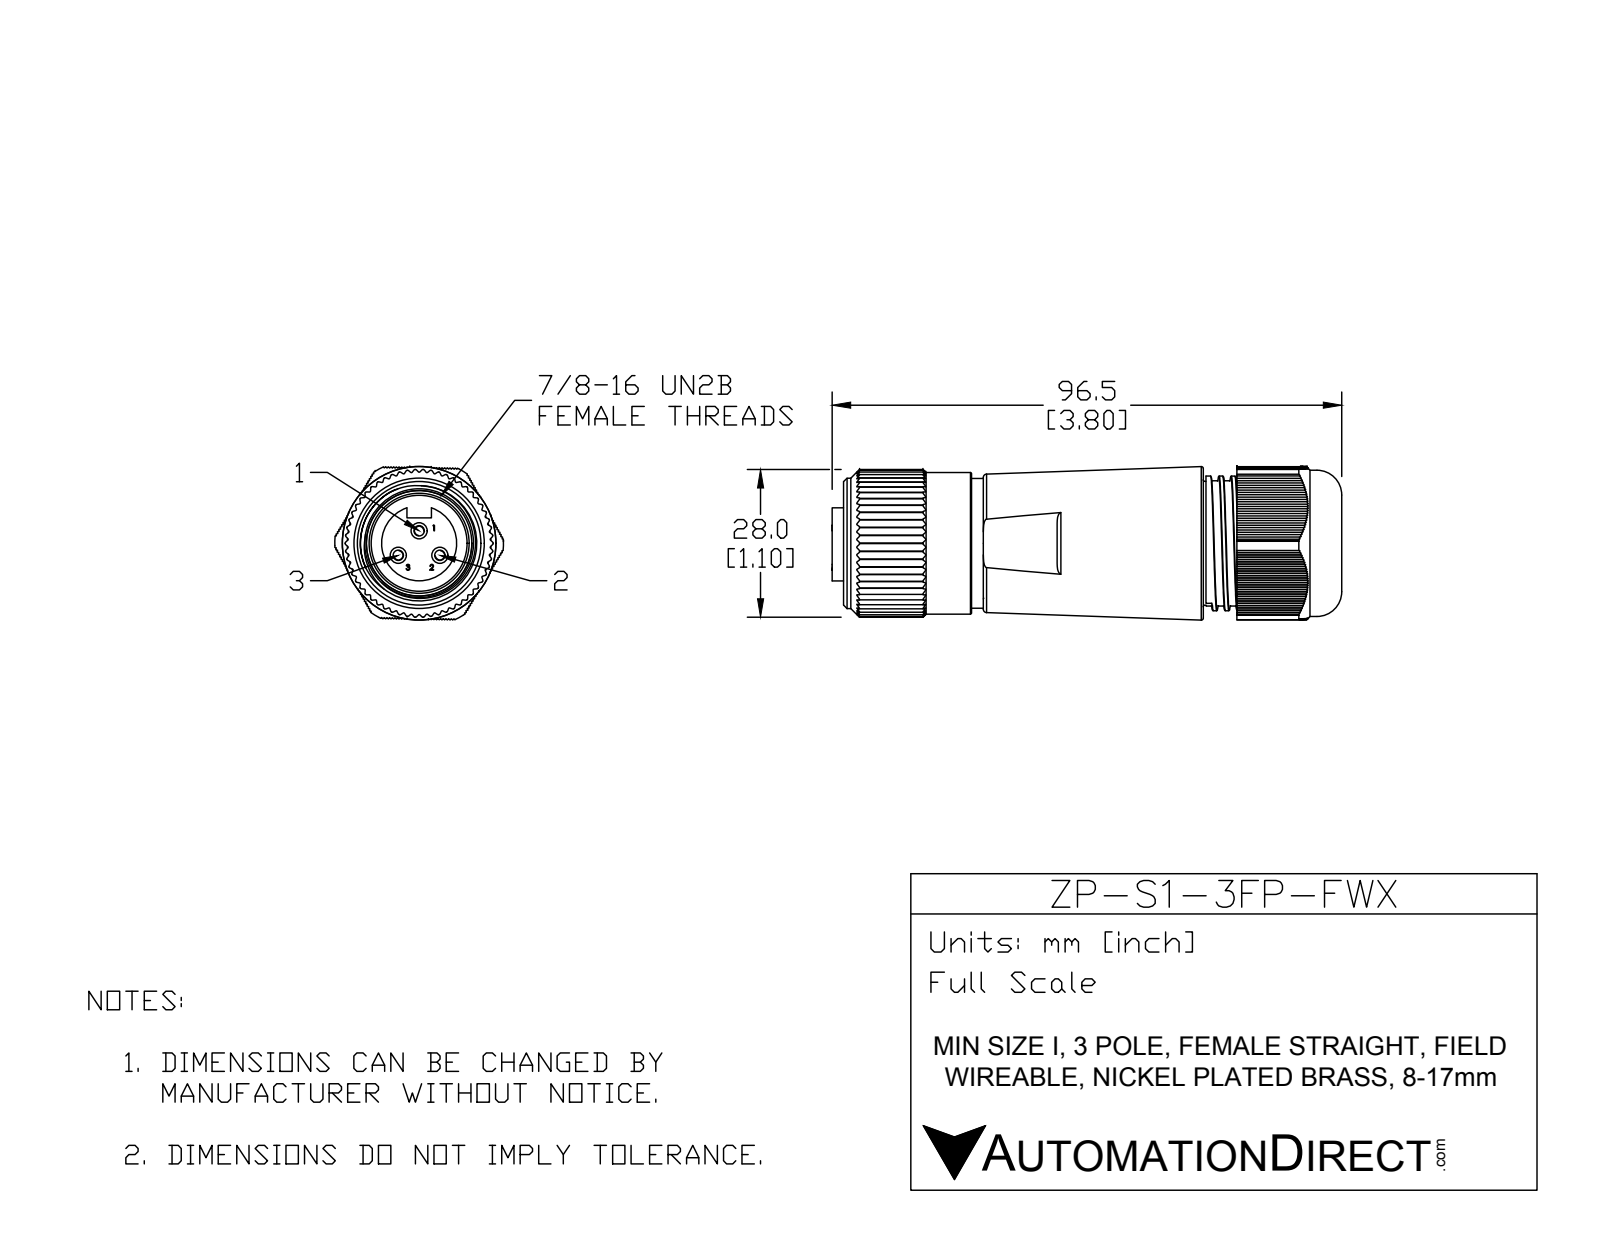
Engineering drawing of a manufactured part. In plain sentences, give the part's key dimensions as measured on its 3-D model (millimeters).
The part is named "MIN-3FP-FWX". Its 3-D file was written by "SolidWorks 2015 (AUTOMOTIVE_DESIGN)". It is 1 solid with 1065 faces: 669 planar, 335 cylindrical and 61 other. Overall it measures 96.54 by 31.9 by 29.06 millimeters. Its volume is 53 715 cubic millimeters and its surface area 15 695 square millimeters. Round holes: 3 of diameter 3.05, 1 of diameter 3.5, 1 of diameter 17.27, 1 of diameter 20.57, 1 of diameter 24.13, 1 of diameter 25.4. Round bosses or shafts: 1 of diameter 27.69, 1 of diameter 26.8, 1 of diameter 25.5, 1 of diameter 24.68, 1 of diameter 24.56, 1 of diameter 24, 1 of diameter 18.14, 1 of diameter 14.22. Partial cylindrical surfaces (rounded edges, fillets, slot ends): 116 of radius 0.25, 58 of radius 0.2, 1 of radius 14, 1 of radius 15.95. The main face-to-face distances are 0.36, 0.72, 1.08, 18.94, 18.92, 1.44, 17.89, 0.5, 6.35, 24.24. The hole center spacings are 4.54, 6.07, 2.36, 7.88.
